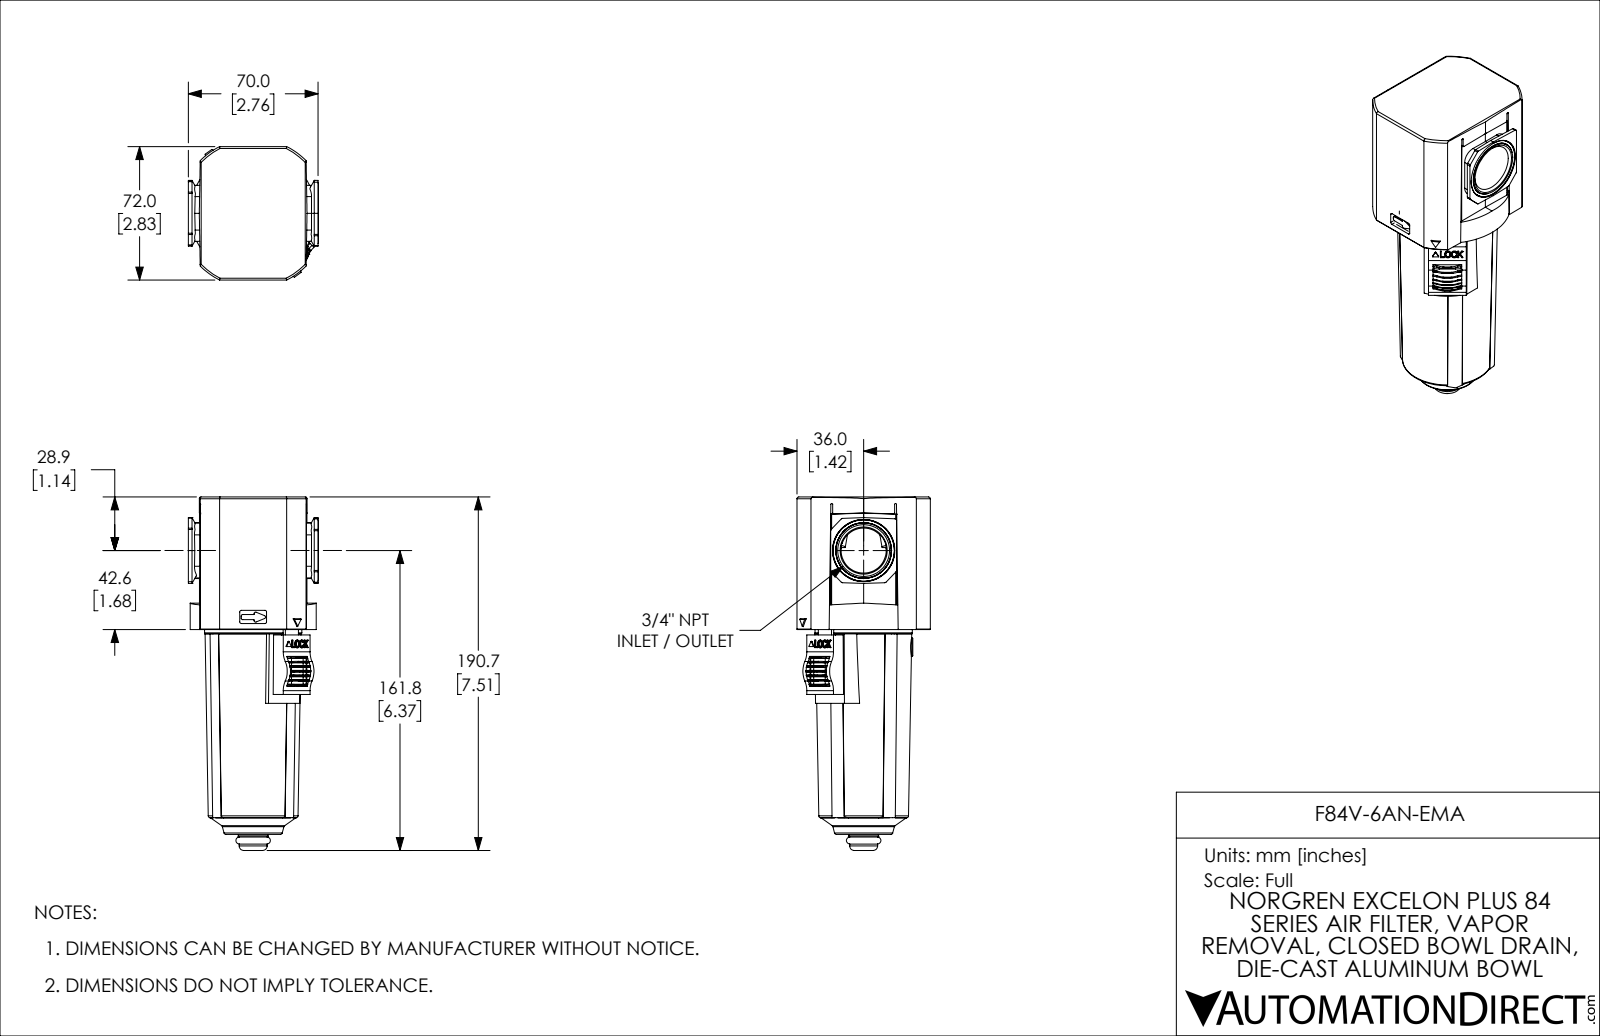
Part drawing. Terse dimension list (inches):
name: F84V-6AN-EMA
written by: SolidWorks 2021 (CONFIG_CONTROL_DESIGN)
unit: in
bodies: 5 solids, 998 faces (416 planar, 364 cylindrical, 218 other)
size: 7.508 × 2.835 × 2.766
volume: 26.49 in³; area: 148.5 in²
holes: 2× ⌀0.163, 1× ⌀0.126, 1× ⌀0.268, 1× ⌀0.633, 1× ⌀2.461
bosses: 2× ⌀0.315, 2× ⌀0.276, 1× ⌀2.122, 1× ⌀2.067, 1× ⌀2.018, 1× ⌀1.959, 1× ⌀1.953, 1× ⌀0.906
rounds: 46× R0.039, 37× R0.02, 16× R0.028, 14× R0.01, 8× R0.008, 8× R0.038, 8× R0.045, 8× R0.06
face distances: 0.059, 2.411, 2.352, 2.047, 2.835, 1.988, 0.364, 2.756, 0.404, 0.768
hole spacings: 0.594, 1.189
